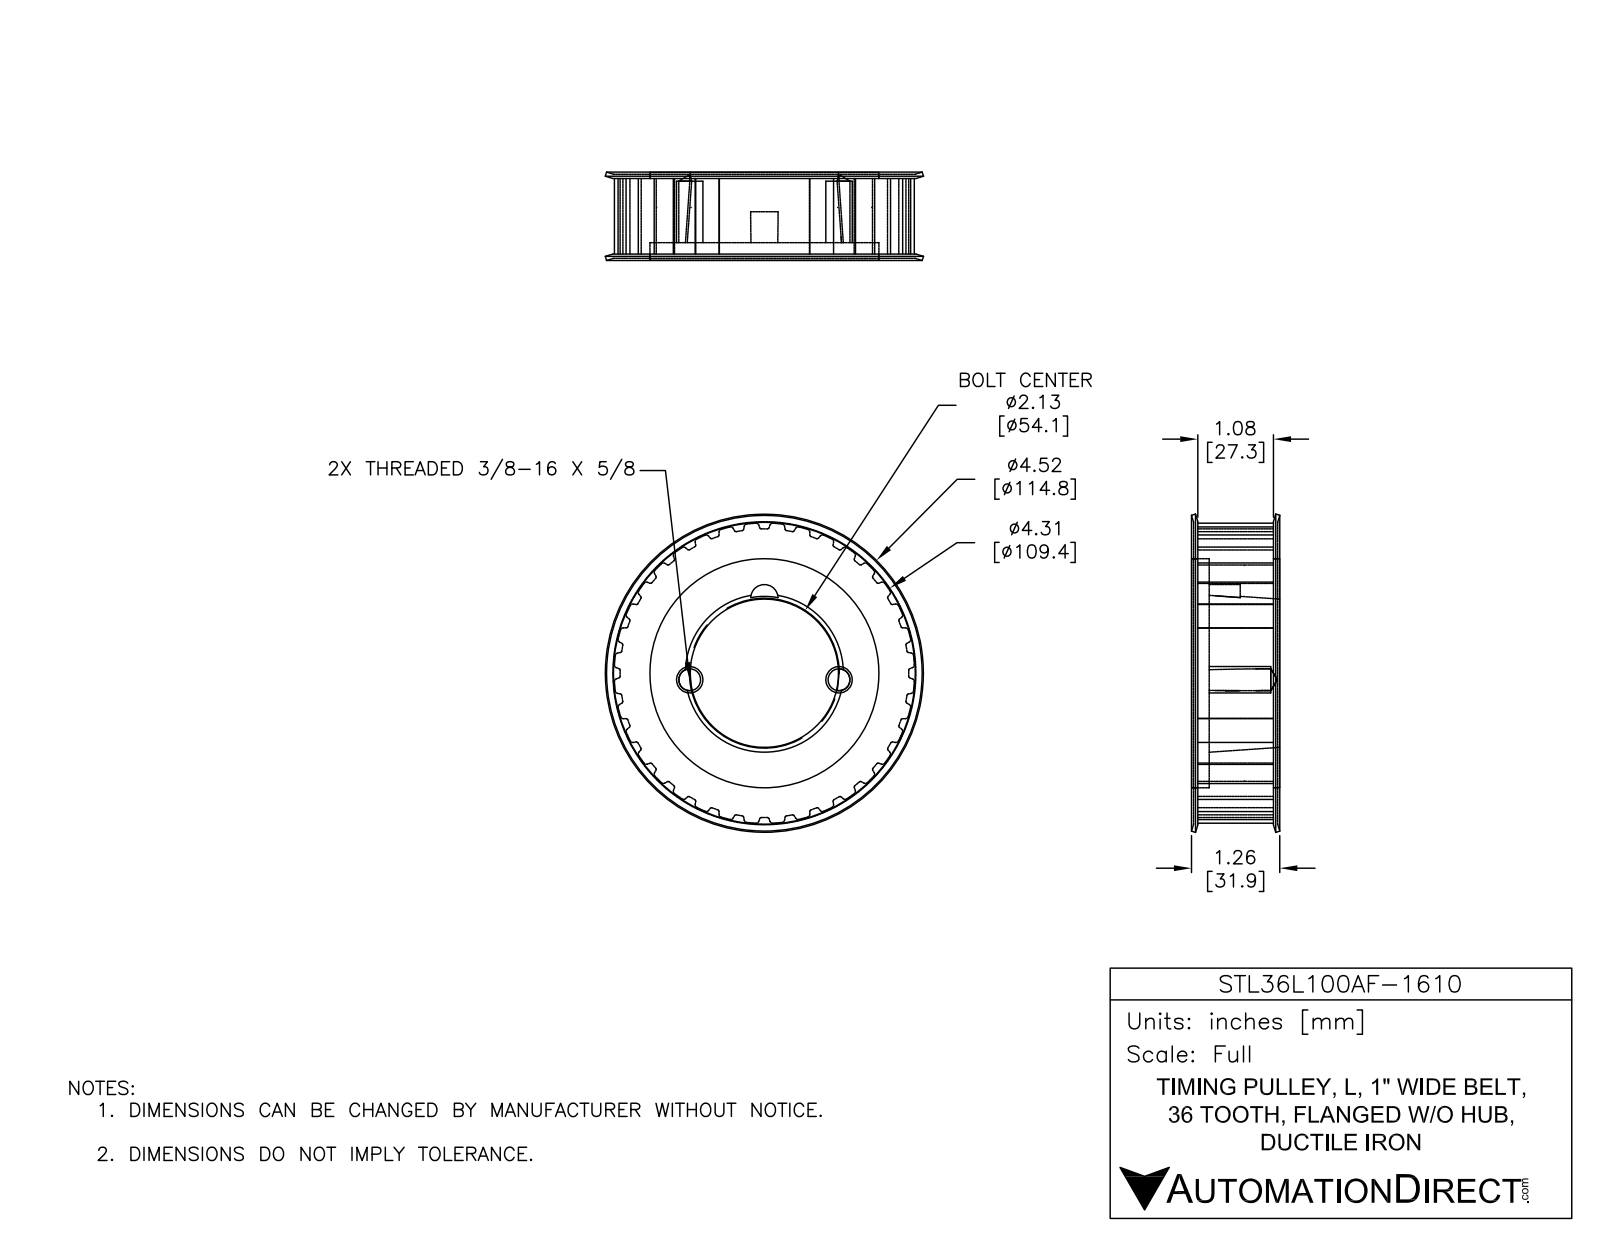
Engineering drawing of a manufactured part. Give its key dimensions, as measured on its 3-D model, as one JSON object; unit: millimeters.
{"part_name": "STL36L100AF-1610", "step_written_by": "SolidWorks 2018 (AUTOMOTIVE_DESIGN)", "units": "millimeters", "bodies": {"solids": 1, "faces": 355, "planar": 116, "cylindrical": 221, "other": 18}, "overall_size": [114.77, 114.77, 29.66], "volume_mm3": 175662, "surface_area_mm2": 36740, "round_holes": [[82.7, 1]], "round_bosses_or_shafts": [[94.7, 1]], "partial_cylinders_radius": [[0.38, 72], [0.51, 72], [3.94, 2], [4.95, 1], [54.2, 1]], "face_to_face_distances": [23.18, 0.7, 22.48, 28.84, 28.14, 5.66, 29.53, 28.83, 6.35, 0.69]}
